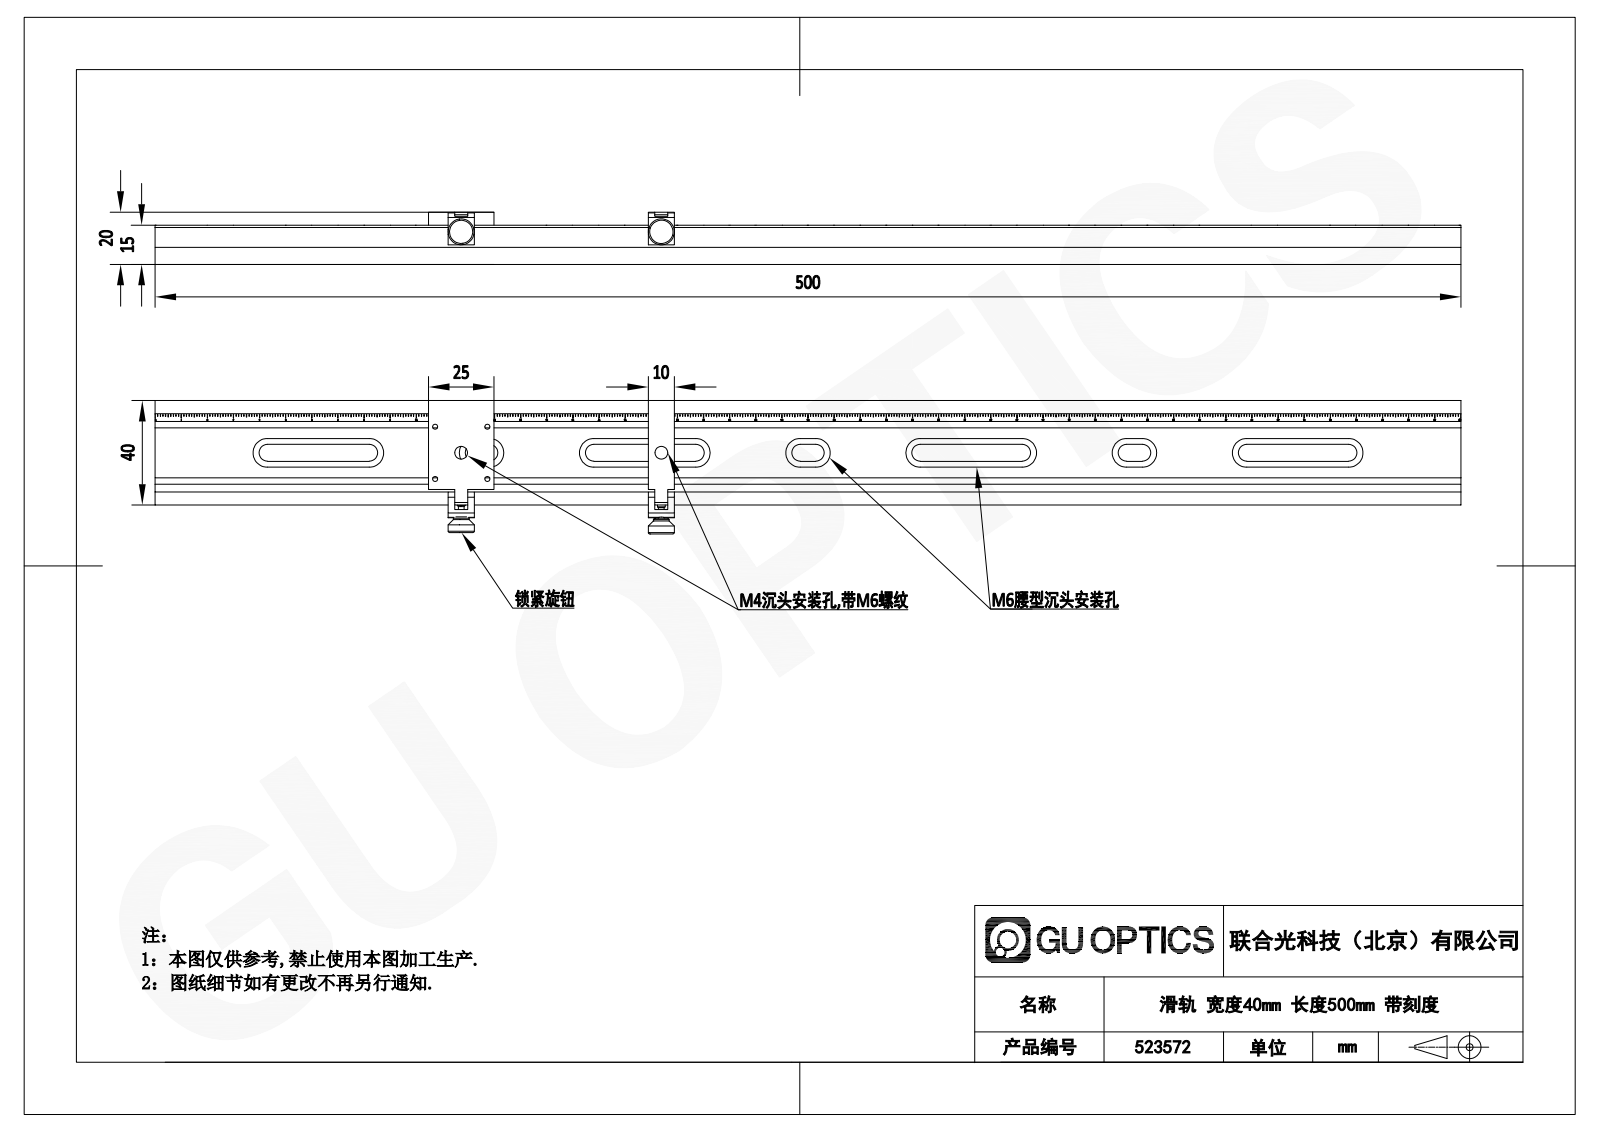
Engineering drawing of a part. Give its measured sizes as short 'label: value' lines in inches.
name: 523572
written by: SolidWorks 2020 (CONFIG_CONTROL_DESIGN)
unit: in
bodies: 8 solids, 4916 faces (3825 planar, 99 cylindrical, 992 other)
size: 19.685 × 2.009 × 0.787
volume: 11.34 in³; area: 113.9 in²
holes: 4× ⌀0.081, 2× ⌀0.098, 2× ⌀0.126, 2× ⌀0.197, 2× ⌀0.315, 1× ⌀0.059, 1× ⌀0.079
bosses: 2× ⌀0.394, 2× ⌀0.236, 2× ⌀0.118, 2× ⌀0.087
rounds: 14× R0.128, 14× R0.217, 1× R0.049, 1× R0.098, 1× R0.177, 1× R0.492
face distances: 0.236, 0.571, 0.02, 0.256, 0.591, 0.197, 0.335, 1.575, 0.315, 0.374
hole spacings: 0.557, 0.787, 1.113, 2.652, 3.017, 3.433
